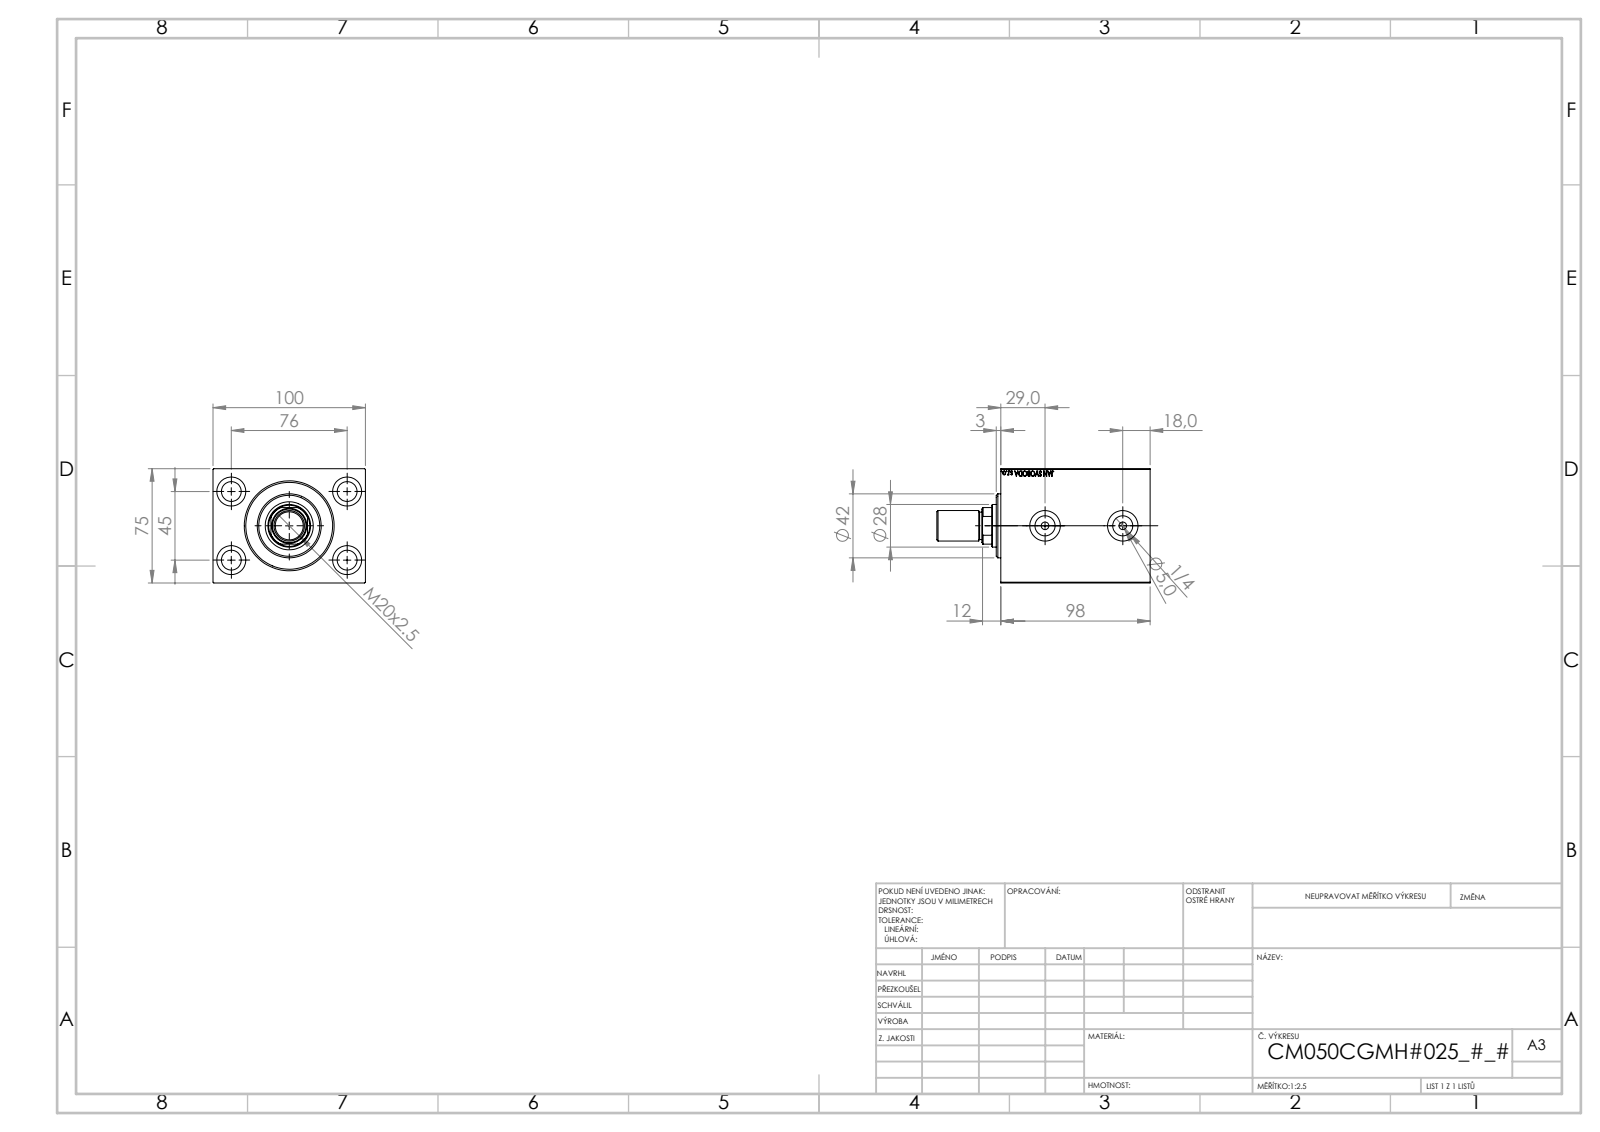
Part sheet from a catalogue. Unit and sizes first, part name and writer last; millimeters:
Units: millimetres
Overall size (bounding box): 140 × 100 × 75
Round holes (diameter × count): ⌀13 ×4, ⌀19 ×4, ⌀5 ×2, ⌀13.16 ×2, ⌀20 ×2, ⌀18.5 ×1, ⌀28 ×1, ⌀31.5 ×1, ⌀50 ×1, ⌀52 ×1, ⌀57 ×1
Round bosses / shafts (diameter × count): ⌀42 ×1, ⌀20 ×1, ⌀18 ×1
Partial cylindrical surfaces — rounded edges, fillets, slot ends (radius × count): R13.5 ×1
Main face-to-face distances: 75, 100, 98, 84, 14, 25, 29.3, 54.7, 68.7, 54.3
Hole centre spacings: 44.16, 45, 76, 88.32, 51
Volume: 640 263 mm³ · Surface area: 111 501 mm²
Bodies: 4 solids, 879 faces (413 planar, 66 cylindrical, 400 other)
Part name (STEP PRODUCT): V450CM_C_Body; V450CM_MALE_METRIC; V450CM_C_VCP; V450CM_VC_B
STEP written by: SolidWorks 2019 (CONFIG_CONTROL_DESIGN)
